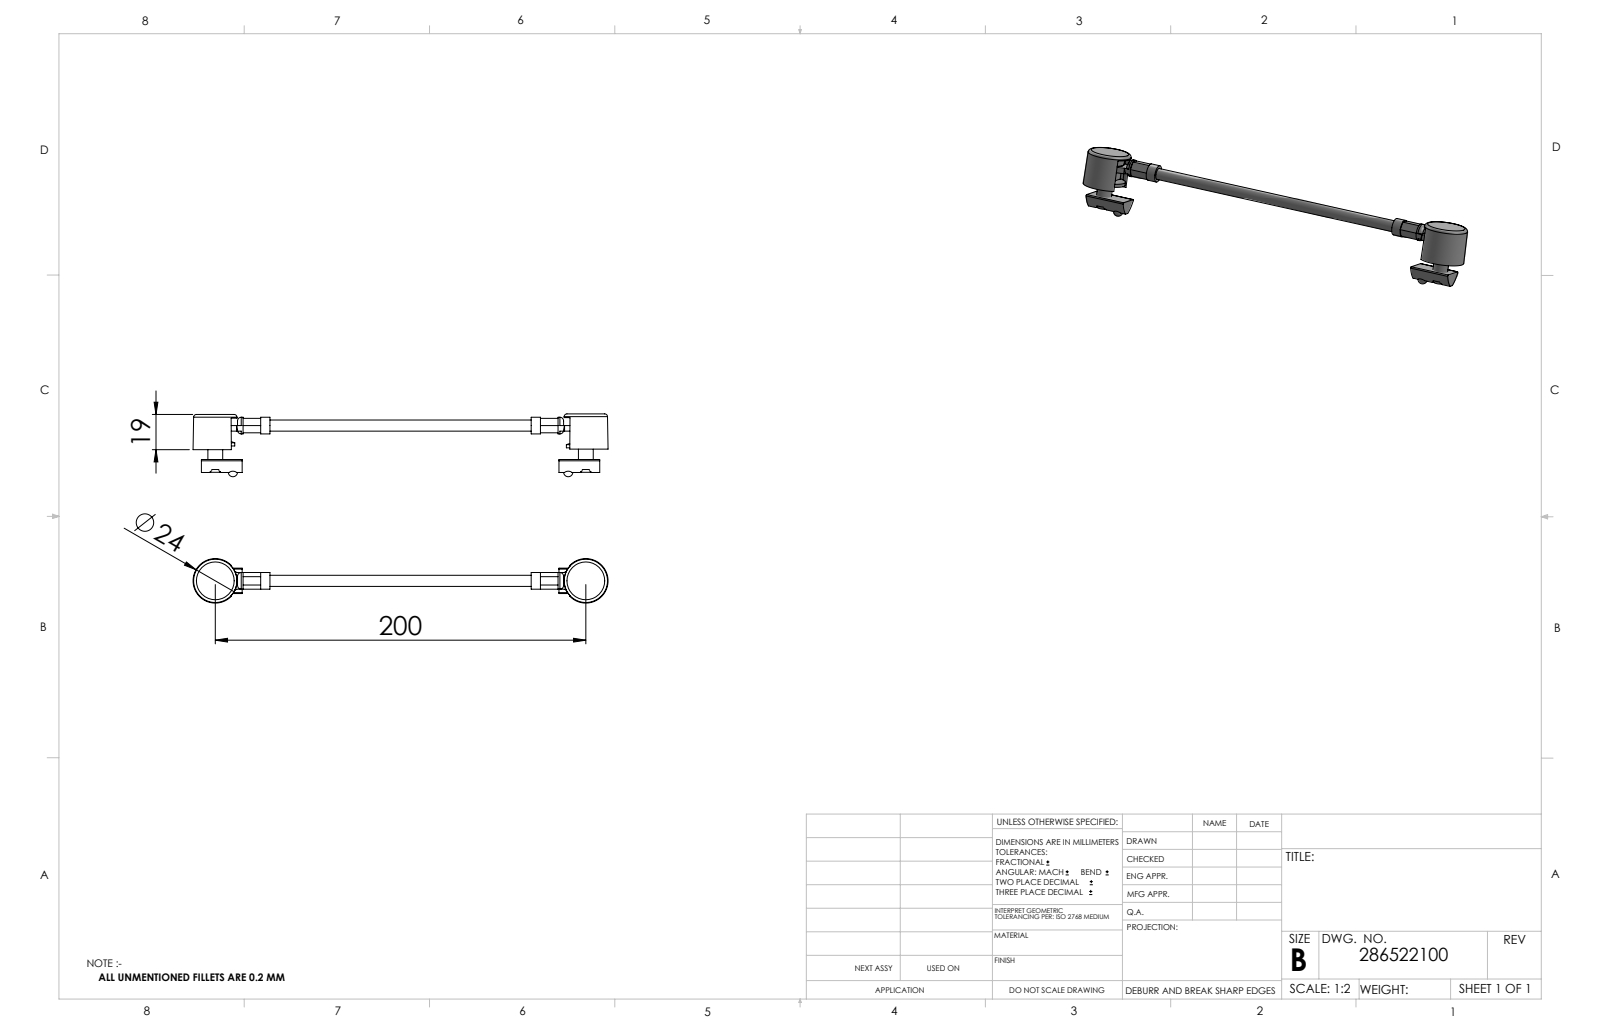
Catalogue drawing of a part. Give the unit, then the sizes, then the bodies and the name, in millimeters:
Units: millimetres
Overall size (bounding box): 224 × 33.82 × 24
Round holes (diameter × count): ⌀6.65 ×2, ⌀6.8 ×2, ⌀8 ×2, ⌀8.4 ×2
Round bosses / shafts (diameter × count): ⌀21 ×2, ⌀15 ×2, ⌀9 ×1, ⌀6 ×1
Partial cylindrical surfaces — rounded edges, fillets, slot ends (radius × count): R0.2 ×4, R1 ×4, R24.07 ×4, R0.5 ×2, R10 ×2, R15 ×2
Main face-to-face distances: 18.3, 9, 7.8, 1, 6.3, 4, 3, 8, 1.5, 15.3
Hole centre spacings: 200
Volume: 21 100 mm³ · Surface area: 19 293 mm²
Bodies: 13 solids, 332 faces (112 planar, 68 cylindrical, 152 other)
Part name (STEP PRODUCT): 093099S01ISO4035M8; 093099S01EL; 286522100_c_1; 093099S01D916M8x30 (+4 more)
STEP written by: SolidWorks 2014 (CONFIG_CONTROL_DESIGN)
